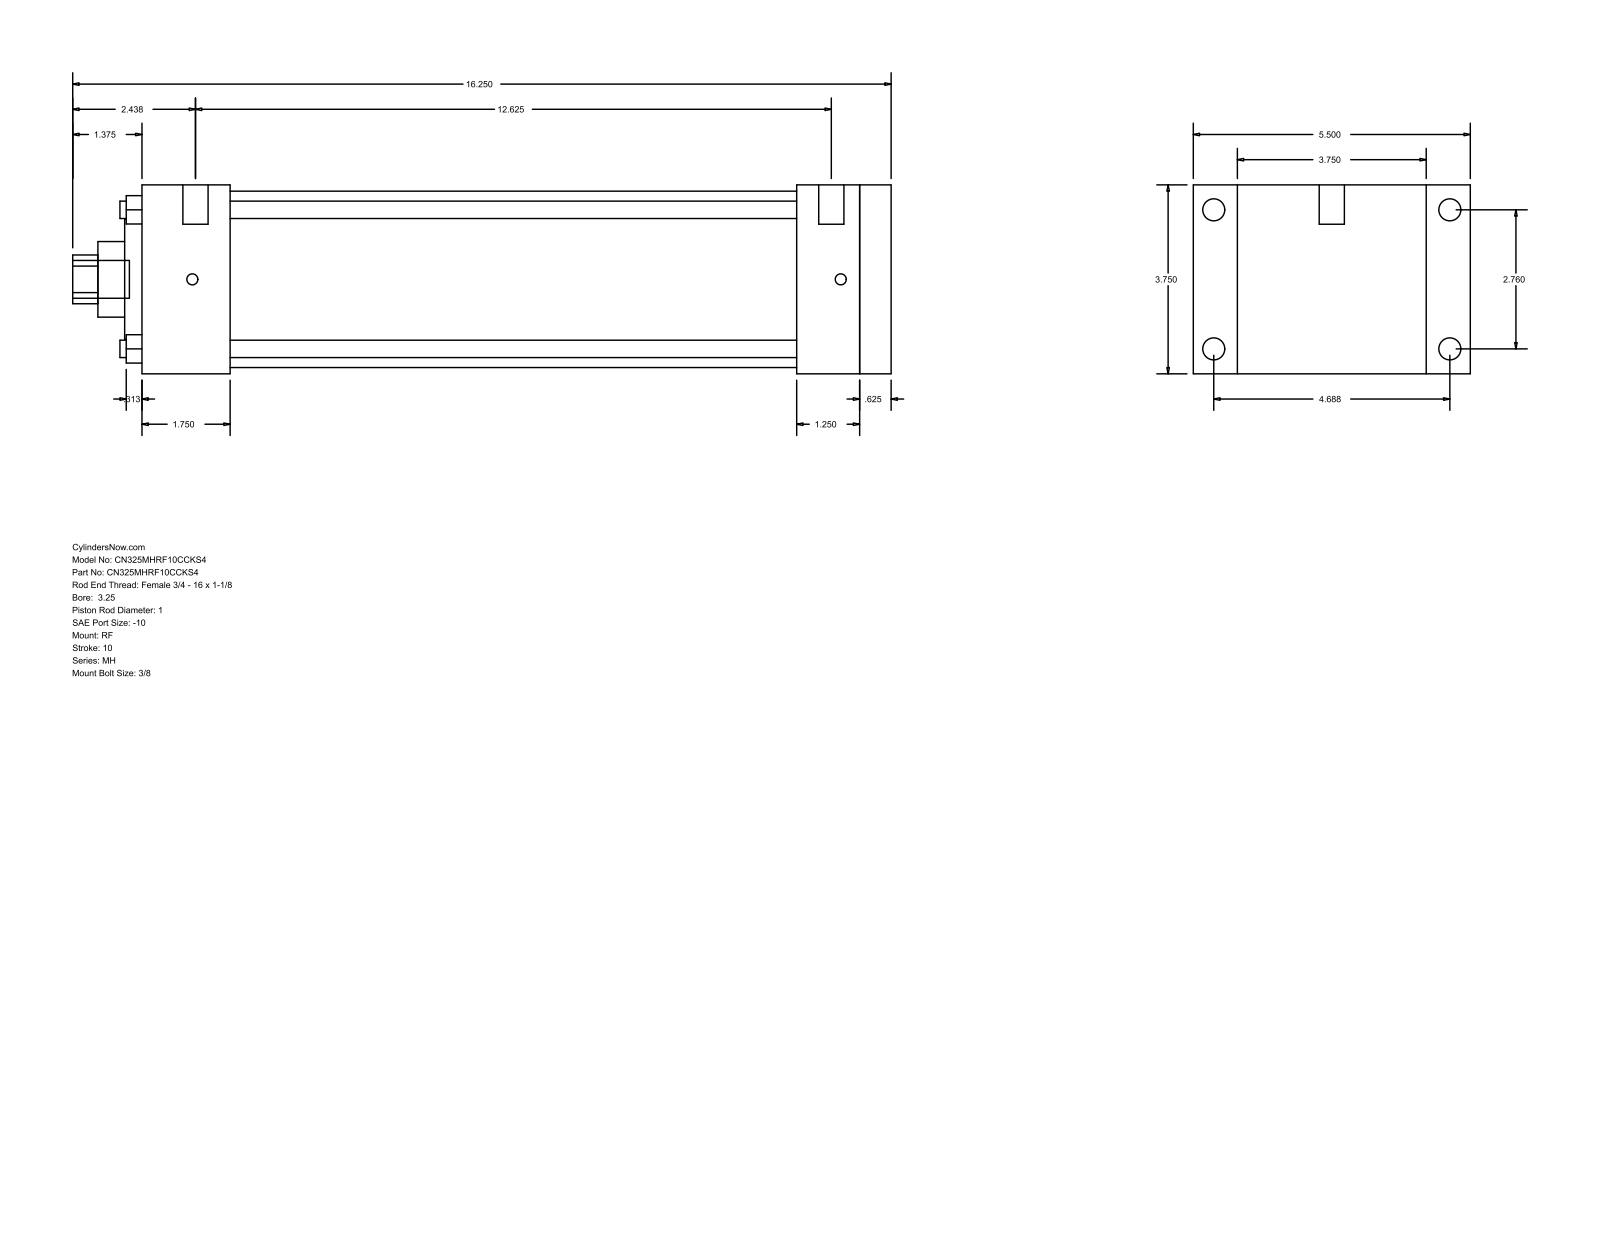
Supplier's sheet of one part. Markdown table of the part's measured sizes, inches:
| quantity | value |
| --- | --- |
| part name | MH_RF__0325_1 |
| STEP written by | GSSL Pune (CONFIG_CONTROL_DESIGN) |
| units | inches |
| bodies | 0 solids, 94 faces (65 planar, 29 cylindrical, 0 other) |
| overall size | 16.25 × 5.5 × 3.75 |
| round holes (diameter × count) | 0.345 × 4, 1 × 1, 1.5 × 1, 2.375 × 1, 3.5 × 1 |
| round bosses / shafts (diameter × count) | 0.438 × 4, 0.219 × 4, 0.5 × 2, 0.75 × 1 |
| partial cylindrical surfaces (radius × count) | 0.484 × 1 |
| main face-to-face distances | 3.75, 14.875, 0.625, 14.25, 0.875, 4.625, 1.75, 12.5, 13.125, 13 |
| hole center spacings | 1.952, 2.76, 3.903 |
